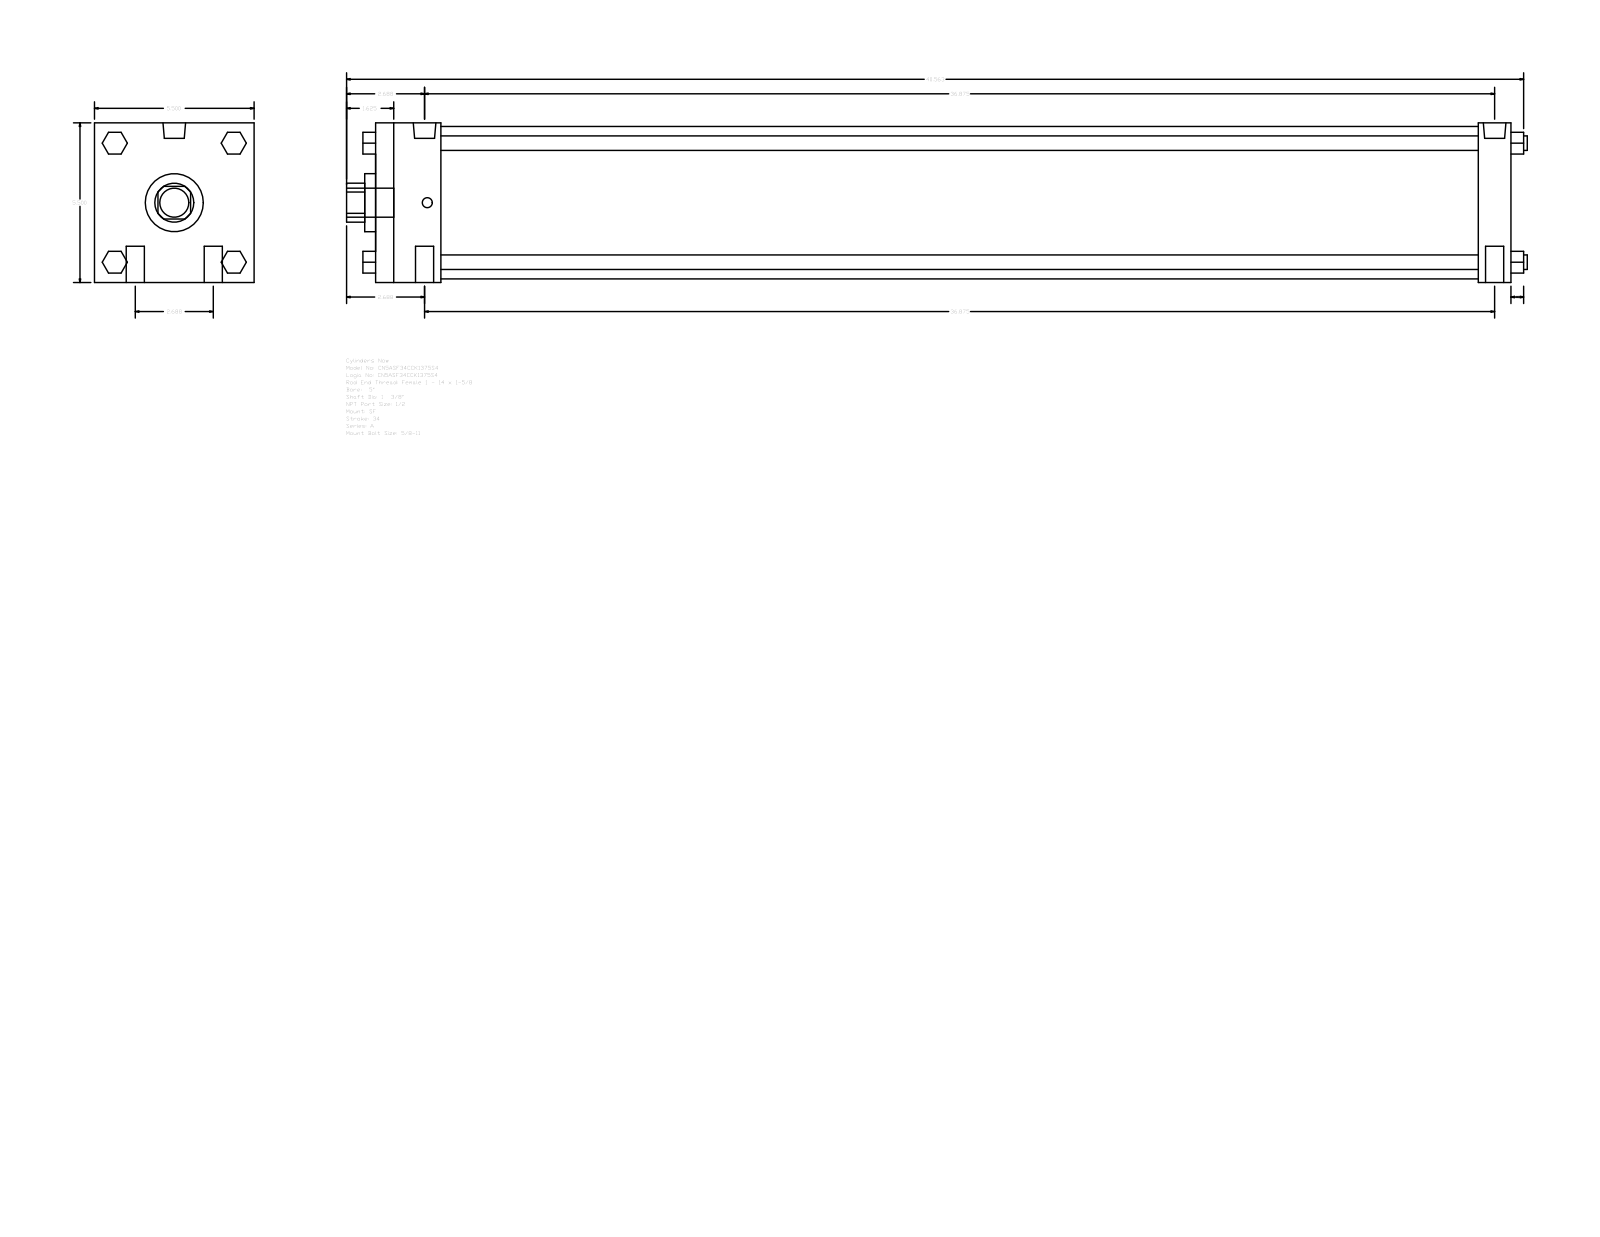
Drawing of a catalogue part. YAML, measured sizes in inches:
part_name: "A_SF__0500_1.375"
step_written_by: "GSSL Pune (CONFIG_CONTROL_DESIGN)"
units: inches
bodies: {solids: 0, faces: 124, planar: 94, cylindrical: 30, other: 0}
overall_size: [40.687, 5.5, 5.5]
round_holes:
  - {diameter: 1.375, count: 1}
  - {diameter: 2, count: 1}
  - {diameter: 5.25, count: 1}
round_bosses_or_shafts:
  - {diameter: 0.625, count: 4}
  - {diameter: 0.5, count: 4}
  - {diameter: 0.778, count: 2}
  - {diameter: 0.344, count: 2}
  - {diameter: 1, count: 1}
partial_cylinders:
  - {radius: 0.672, count: 1}
face_to_face_distances: [5.5, 39.125, 1.125, 2.25, 38, 35.75, 36.875, 0.75, 2.05, 3.55]
